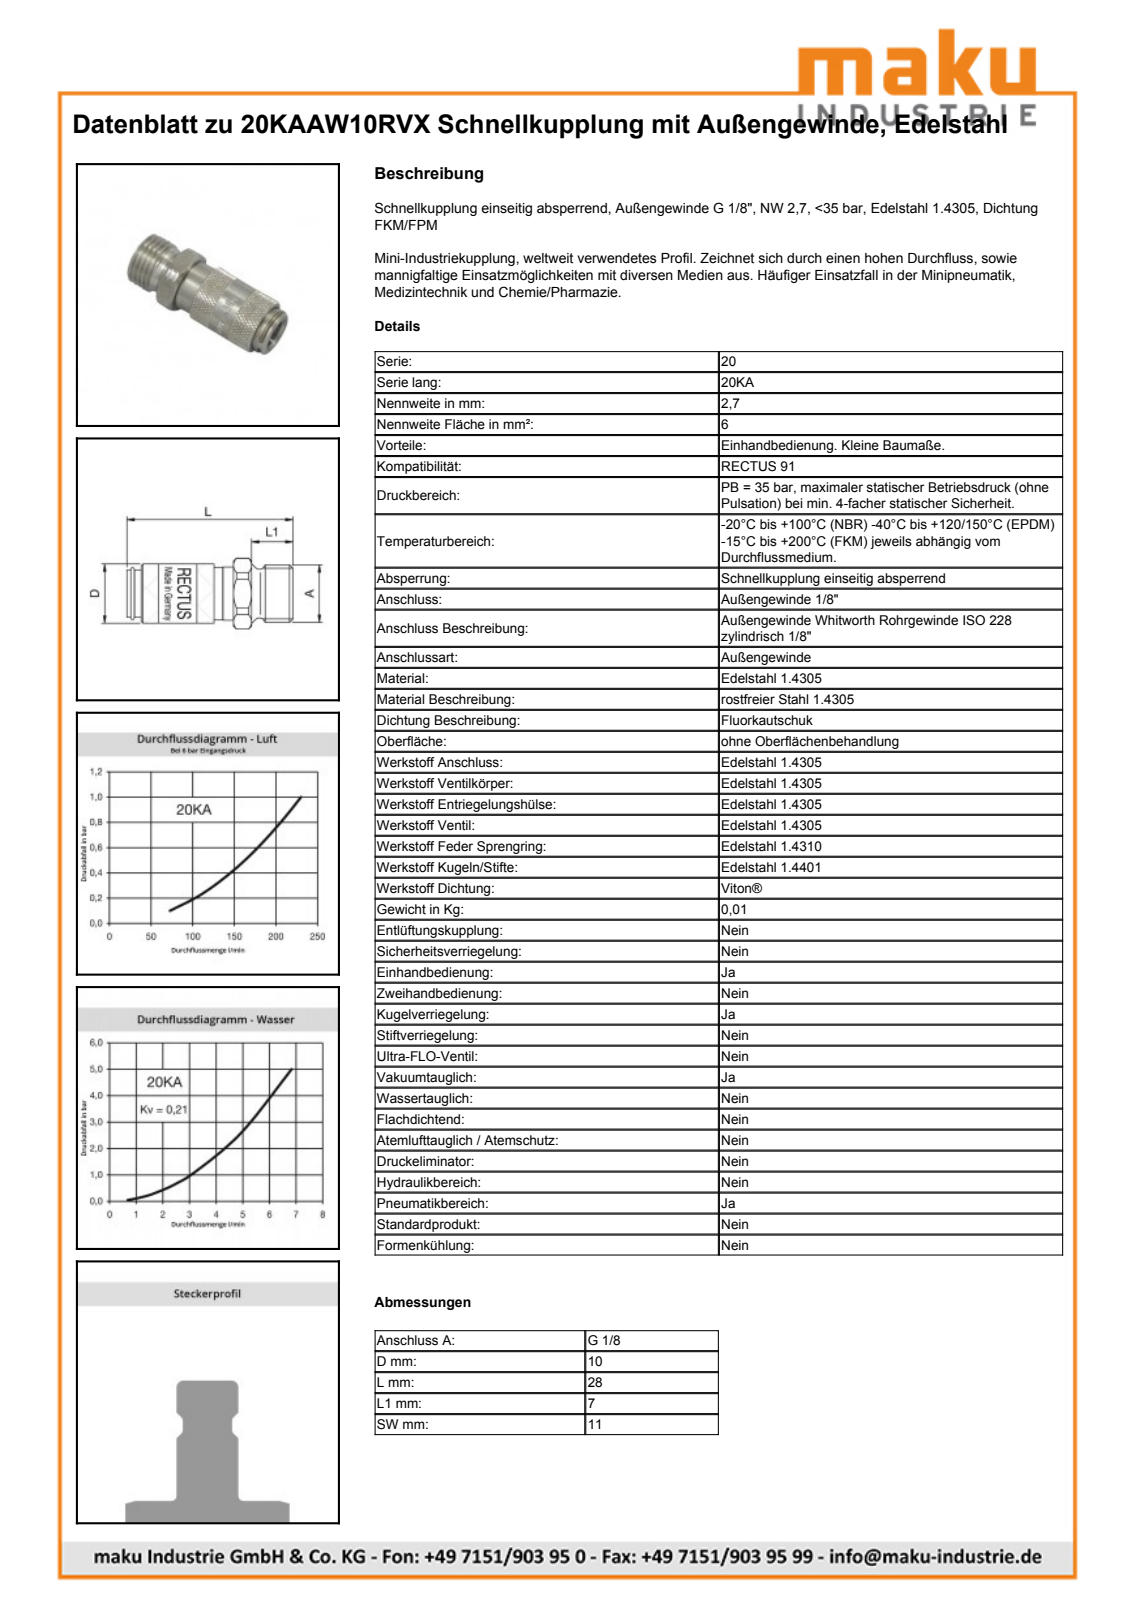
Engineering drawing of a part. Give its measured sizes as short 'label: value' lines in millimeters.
name: D109144
written by: Autodesk Inventor 2013 (AUTOMOTIVE_DESIGN)
unit: mm
bodies: 2 solids, 403 faces (145 planar, 56 cylindrical, 202 other)
size: 28.05 × 11.89 × 11.83
volume: 2 008 mm³; area: 1 957 mm²
holes: 1× ⌀8.1, 1× ⌀8.15, 1× ⌀9.15, 1× ⌀9.2
bosses: 1× ⌀10.35, 1× ⌀10, 1× ⌀9.73, 1× ⌀9, 1× ⌀8, 1× ⌀7.8, 1× ⌀7.61, 1× ⌀7.4
rounds: 1× R4.9, 1× R6
face distances: 28.05, 18, 10.05, 11, 3.3, 13.35, 5, 2.4, 15.6, 25.65
